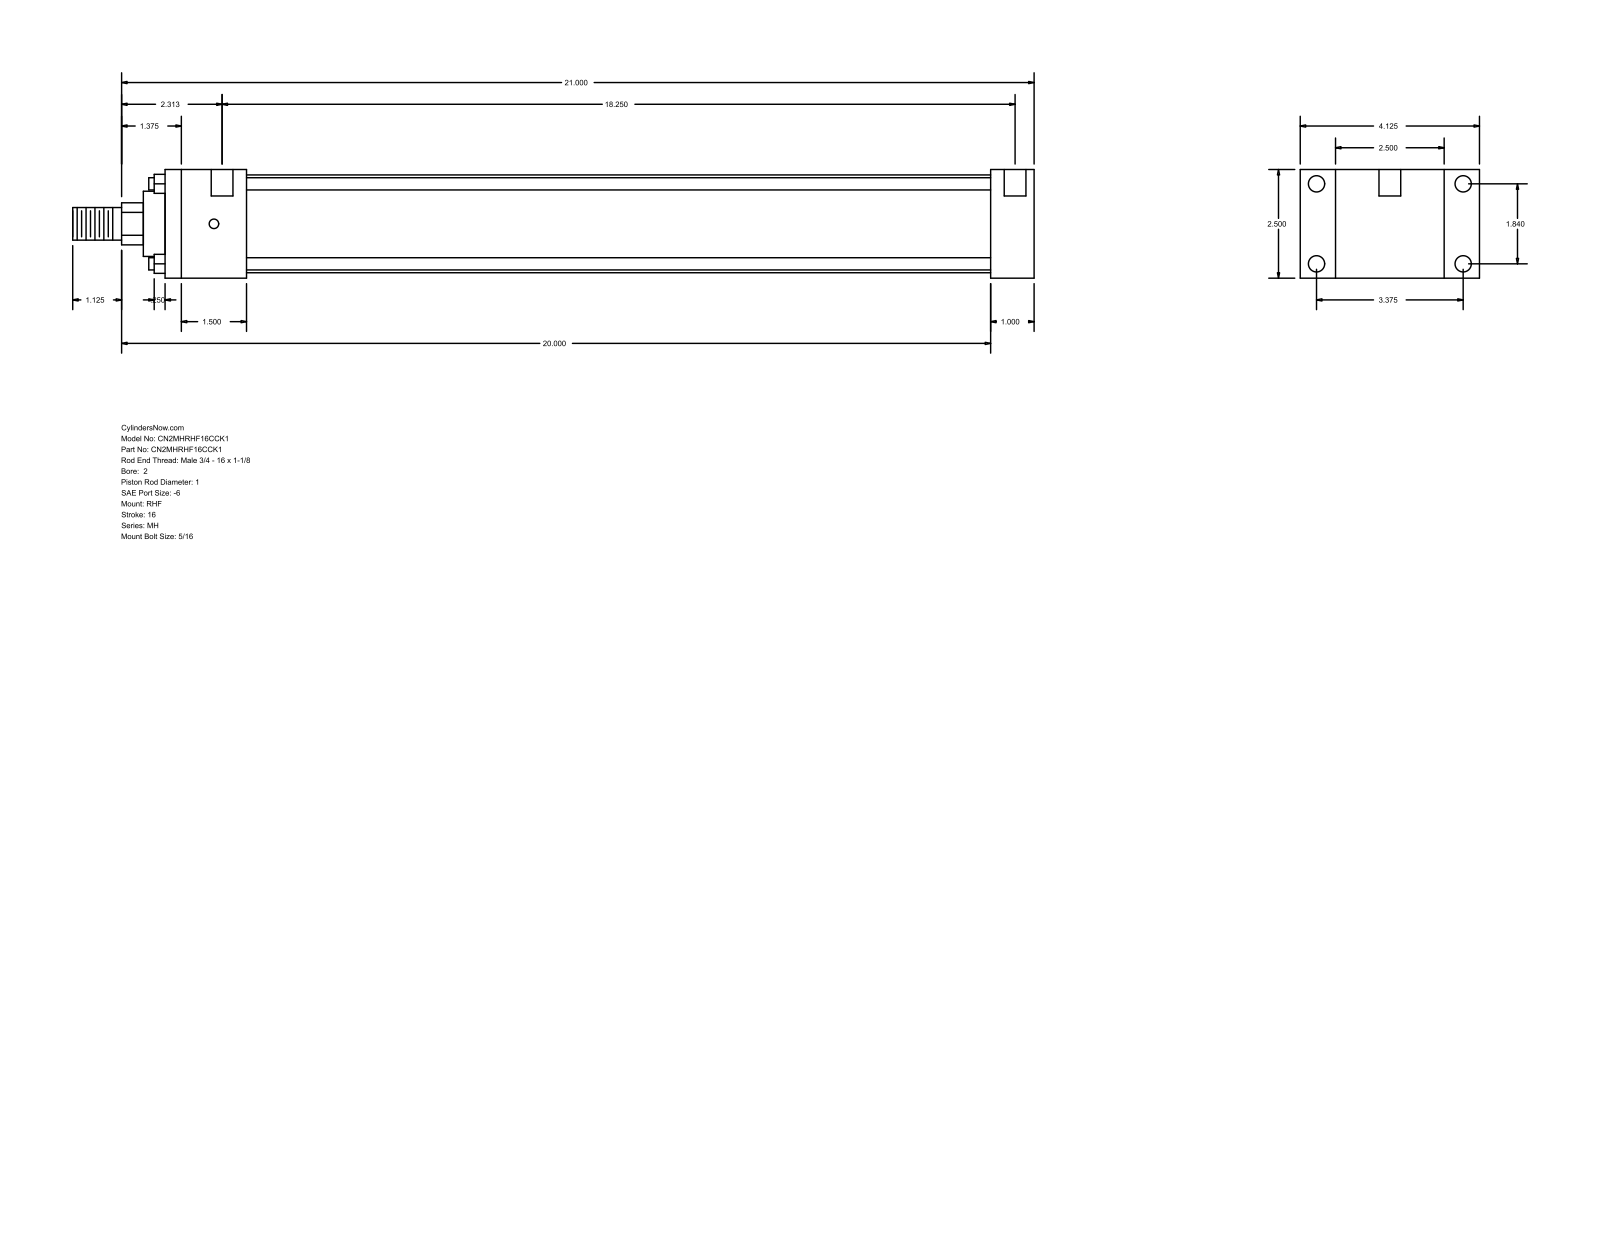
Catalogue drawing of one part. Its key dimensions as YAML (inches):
part_name: "MH_RHF__0200_1"
step_written_by: "GSSL Pune (CONFIG_CONTROL_DESIGN)"
units: inches
bodies: {solids: 0, faces: 88, planar: 60, cylindrical: 28, other: 0}
overall_size: [22.125, 4.125, 2.5]
round_holes:
  - {diameter: 0.219, count: 4}
  - {diameter: 0.375, count: 4}
  - {diameter: 0.5, count: 2}
round_bosses_or_shafts:
  - {diameter: 0.281, count: 4}
  - {diameter: 2.25, count: 1}
  - {diameter: 1.5, count: 1}
  - {diameter: 1, count: 1}
  - {diameter: 0.75, count: 1}
partial_cylinders:
  - {radius: 0.484, count: 1}
face_to_face_distances: [2.5, 1, 0.813, 3.313, 20, 19, 4.125, 1.875, 17.125, 18.125]
hole_center_spacings: [1.84, 3.375, 3.844, 18.562, 0.125, 0.187, 18.25, 18.375]
